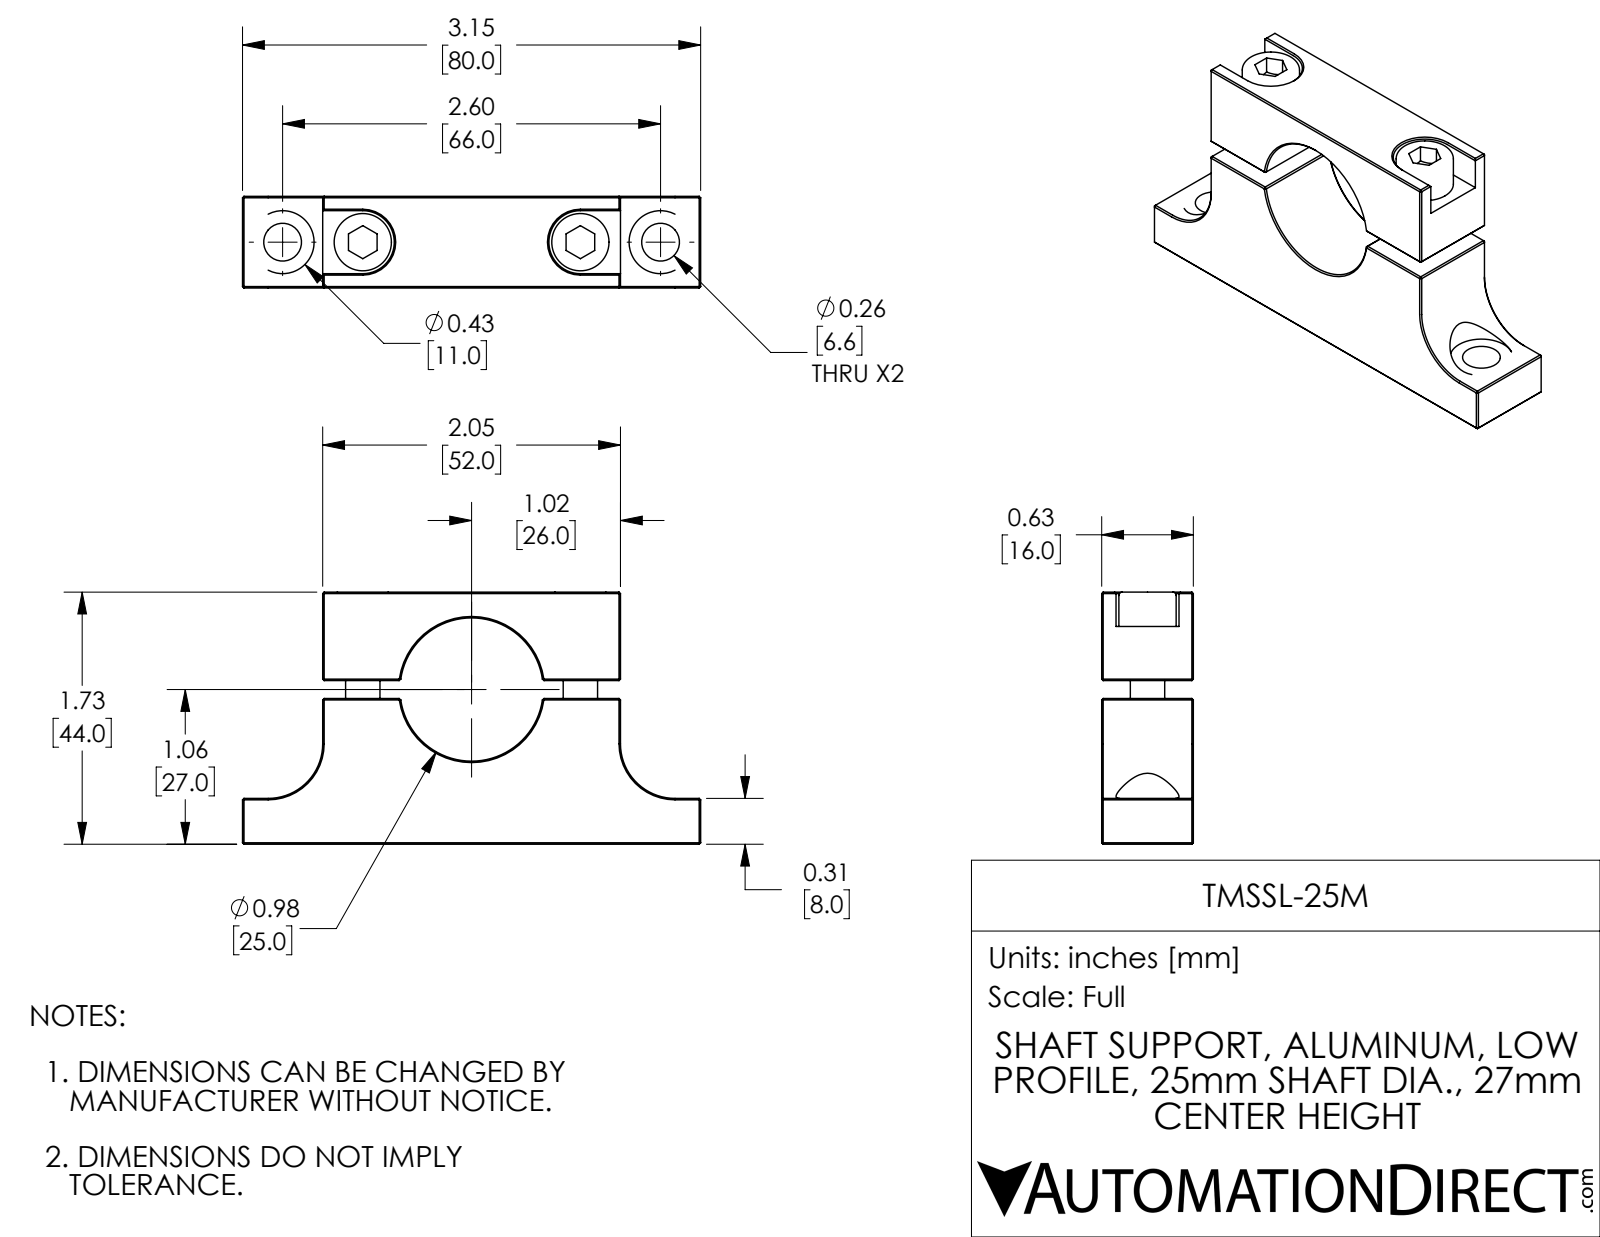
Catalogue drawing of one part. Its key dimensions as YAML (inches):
part_name: "TMSSL-25M"
step_written_by: "SolidWorks 2017 (AUTOMOTIVE_DESIGN)"
units: inches
bodies: {solids: 4, faces: 177, planar: 118, cylindrical: 31, other: 28}
overall_size: [3.15, 1.733, 0.63]
volume: 1.811
surface_area: 19.5
round_holes:
  - {diameter: 0.26, count: 4}
  - {diameter: 0.194, count: 2}
  - {diameter: 0.094, count: 1}
  - {diameter: 0.984, count: 1}
round_bosses_or_shafts:
  - {diameter: 0.394, count: 2}
  - {diameter: 0.236, count: 2}
partial_cylinders:
  - {radius: 0.216, count: 4}
  - {radius: 0.375, count: 2}
face_to_face_distances: [0.63, 1.732, 1.002, 0.731, 1.124, 0.123, 0.608, 2.047, 1.496, 0.495]
hole_center_spacings: [0.551, 0.748, 1.299, 2.047, 1.496, 2.598]
